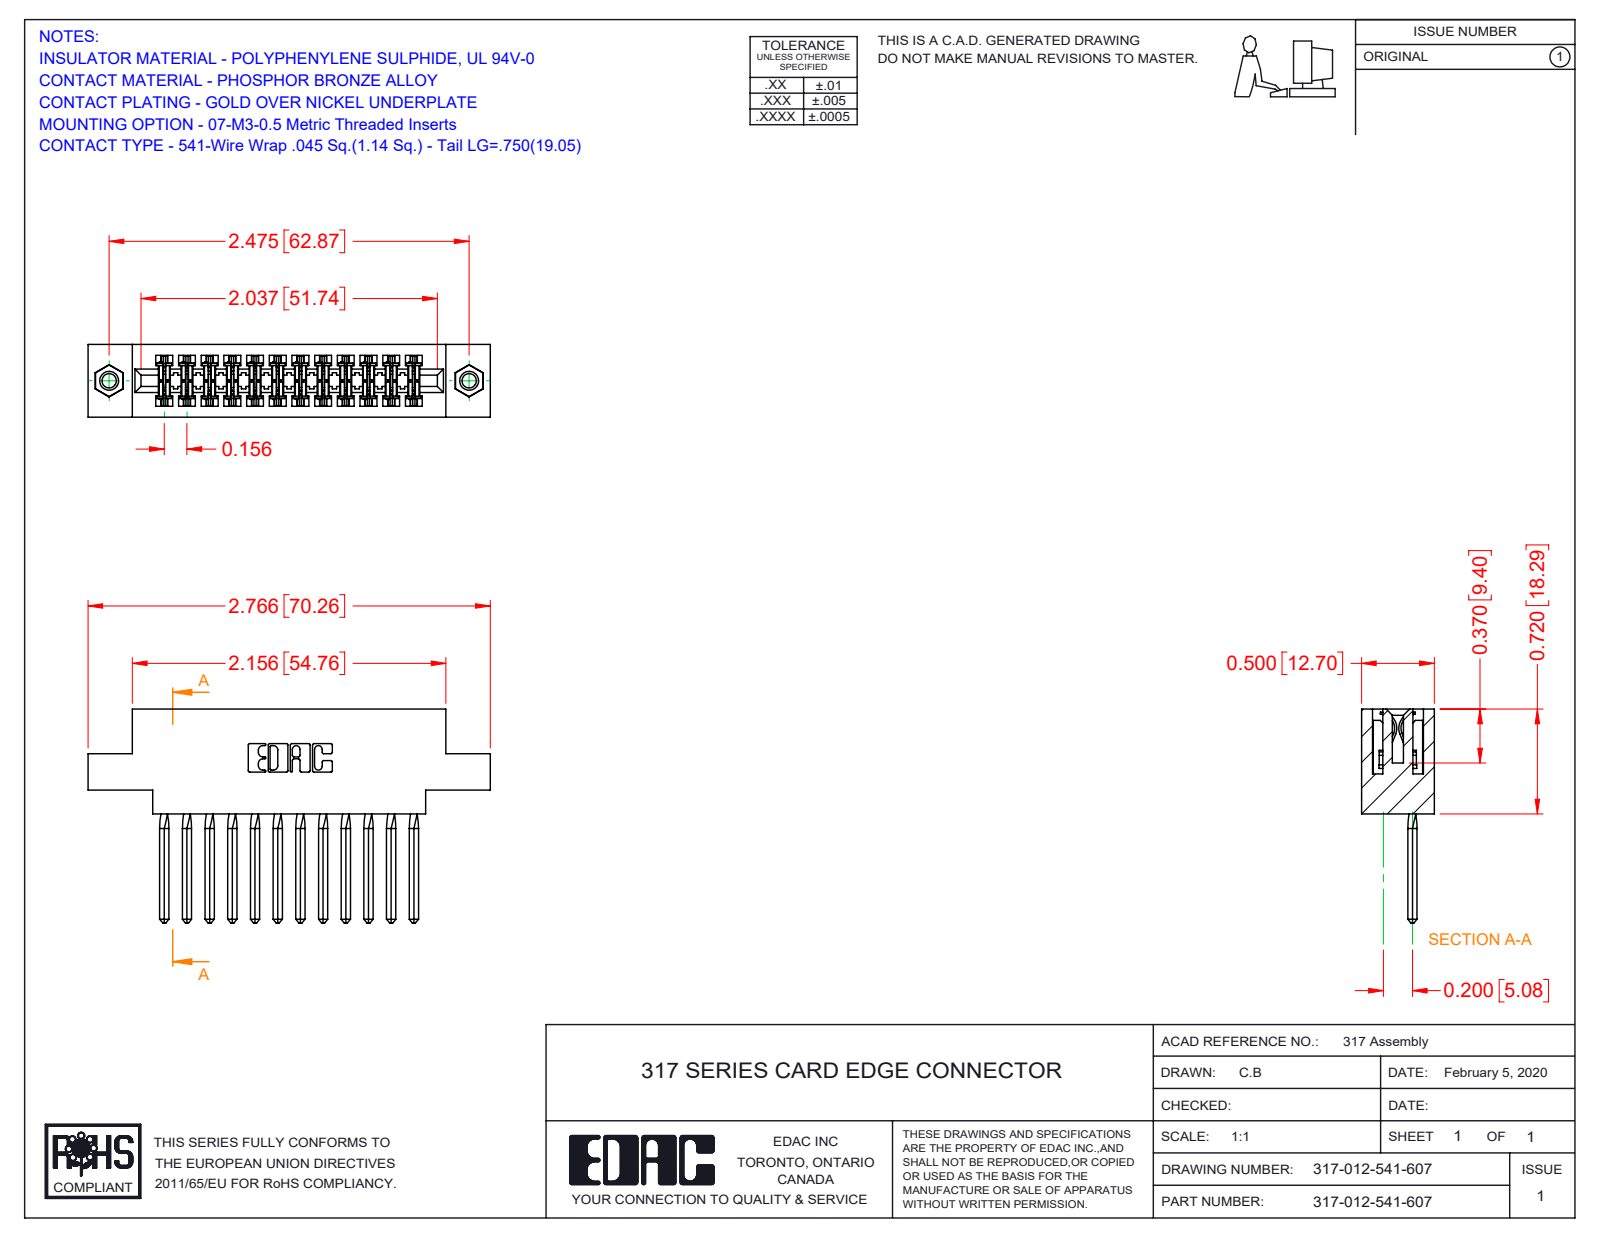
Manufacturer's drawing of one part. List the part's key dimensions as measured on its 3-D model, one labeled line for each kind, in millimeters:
Part name (STEP PRODUCT): 317-012-541-607; 317 Part_.156 Dia - TI; 345-250-001_345-250-005-103; 317-290-002_541
STEP written by: SolidWorks 2016 (CONFIG_CONTROL_DESIGN)
Units: millimetres
Bodies: 15 solids, 1986 faces (1578 planar, 344 cylindrical, 64 other)
Overall size (bounding box): 70.3 × 37.3 × 12.7
Volume: 10 500 mm³ · Surface area: 13 810 mm²
Round holes (diameter × count): ⌀2.5 ×2, ⌀3.2 ×2, ⌀4 ×2
Round bosses / shafts (diameter × count): ⌀3.9 ×2
Partial cylindrical surfaces — rounded edges, fillets, slot ends (radius × count): R0.4 ×24, R0.3 ×22, R0.2 ×6, R0.8 ×6, R0.7 ×3, R2.4 ×2, R2.5 ×2, R2.8 ×2
Main face-to-face distances: 12.7, 1.9, 10.8, 2.8, 5.6, 1.7, 8.9, 8.4, 5, 3.5
Hole centre spacings: 62.9
